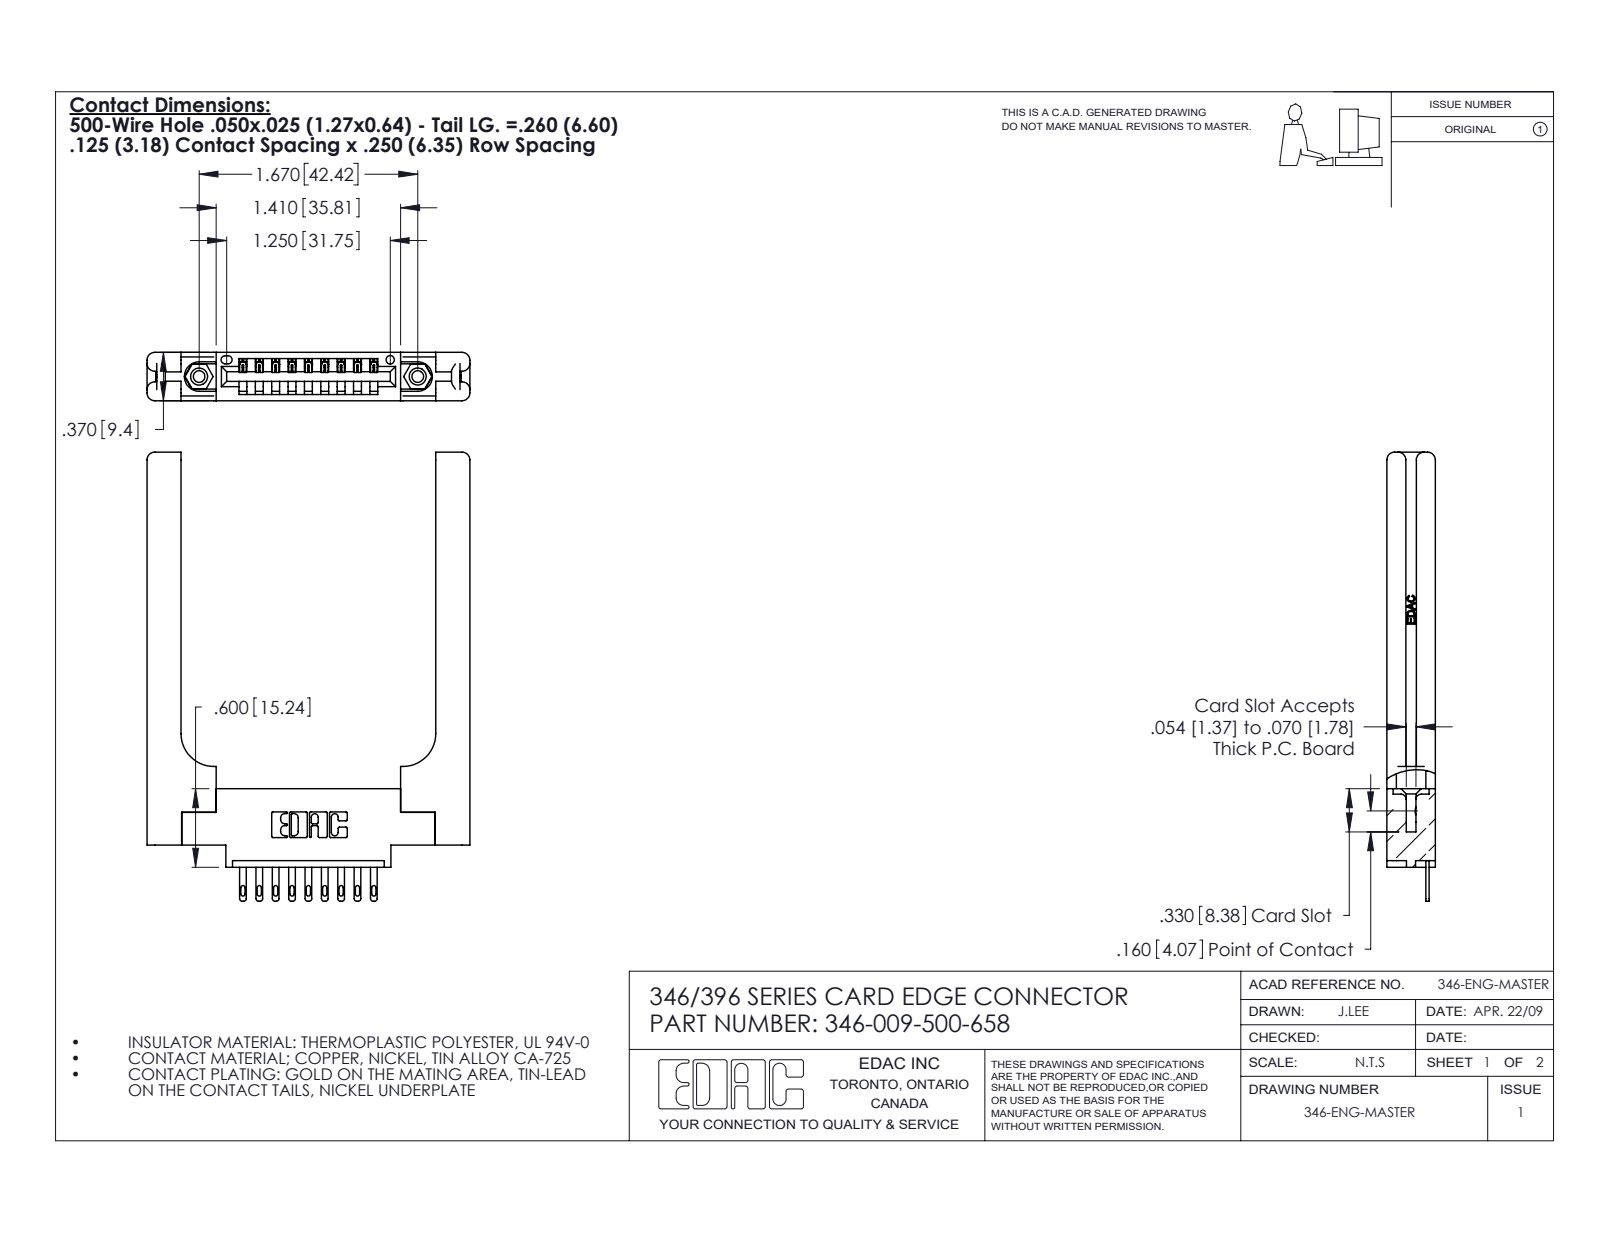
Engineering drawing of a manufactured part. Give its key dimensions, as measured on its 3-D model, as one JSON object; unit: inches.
{"part_name": "345-250-001_345-250-001-102; 346-220-058_345-220-058; 346 Part_0.170 Offset - 0.156 Dia-TH; 346-009-500-658 (+1 more)", "step_written_by": "SolidWorks 2020 (CONFIG_CONTROL_DESIGN)", "units": "inches", "bodies": {"solids": 14, "faces": 882, "planar": 548, "cylindrical": 274, "other": 60}, "overall_size": [3.43, 2.466, 0.37], "volume_in3": 0.801, "surface_area_in2": 18.64, "round_holes": [[0.089, 2], [0.125, 2], [0.156, 2], [0.064, 1]], "round_bosses_or_shafts": [[0.155, 2]], "partial_cylinders_radius": [[0.01, 22], [0.006, 18], [0.016, 18], [0.02, 18], [0.06, 16], [0.007, 6], [0.031, 6], [0.026, 3]], "face_to_face_distances": [0.37, 0.15, 0.072, 0.22, 0.148, 0.102, 0.048, 0.322, 0.173, 0.25], "hole_center_spacings": [0.246, 1.465, 1.67]}
